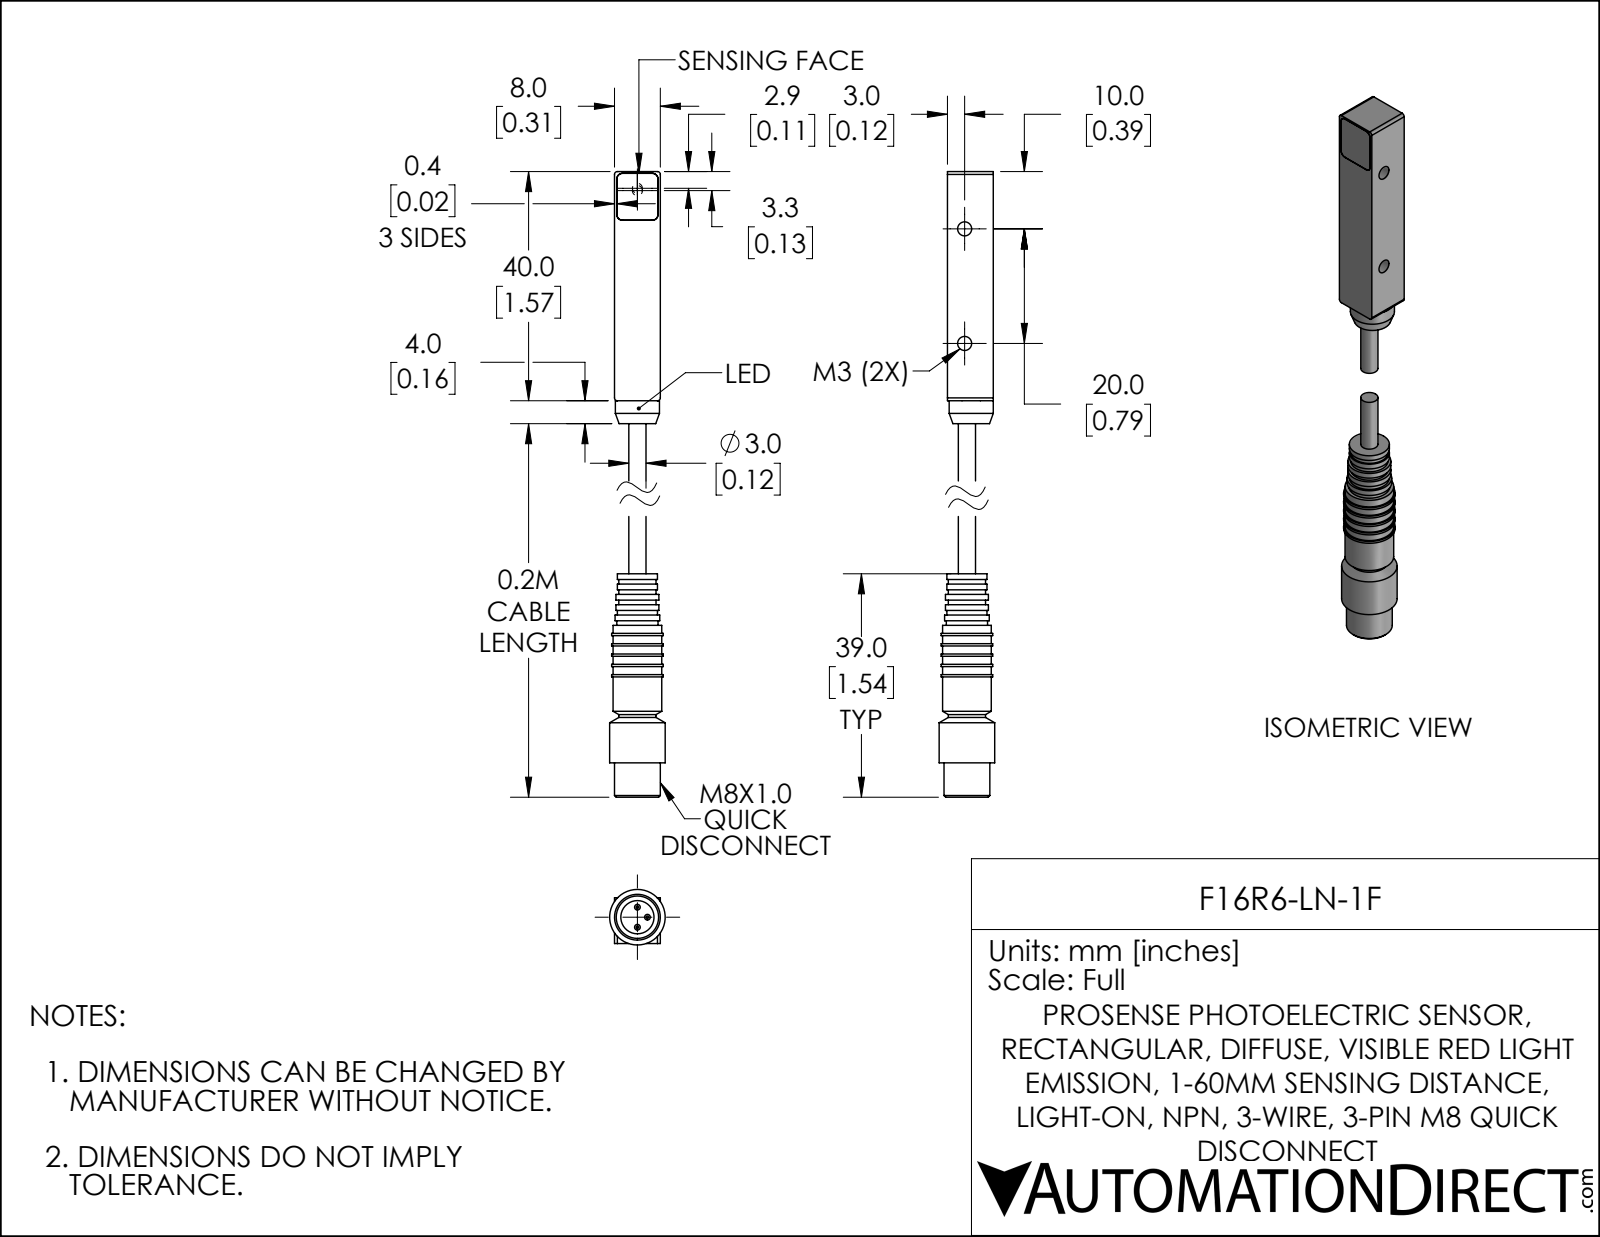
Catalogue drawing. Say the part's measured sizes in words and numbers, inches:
The part is named "F16R6-LN-1F". Its 3-D file was written by "SolidWorks 2019 (CONFIG_CONTROL_DESIGN)". It is 2 solids with 102 faces: 50 planar, 45 cylindrical and 7 other. Overall it measures 4.299 by 0.382 by 0.382 inches. Its volume is 0.293 cubic inches and its surface area 5.017 square inches. Round holes: 2 of diameter 0.097, 1 of diameter 0.228. Round bosses or shafts: 3 of diameter 0.039, 1 of diameter 0.382, 1 of diameter 0.354, 1 of diameter 0.335, 1 of diameter 0.315, 1 of diameter 0.307, 1 of diameter 0.303, 1 of diameter 0.295. Partial cylindrical surfaces (rounded edges, fillets, slot ends): 4 of radius 0.02, 4 of radius 0.039, 4 of radius 0.039. The main face-to-face distances are 0.315, 0.071, 0.142, 0.039, 0.354, 1.732, 1.031, 2.764, 2.37, 0.213. The hole center spacings are 0.787.
